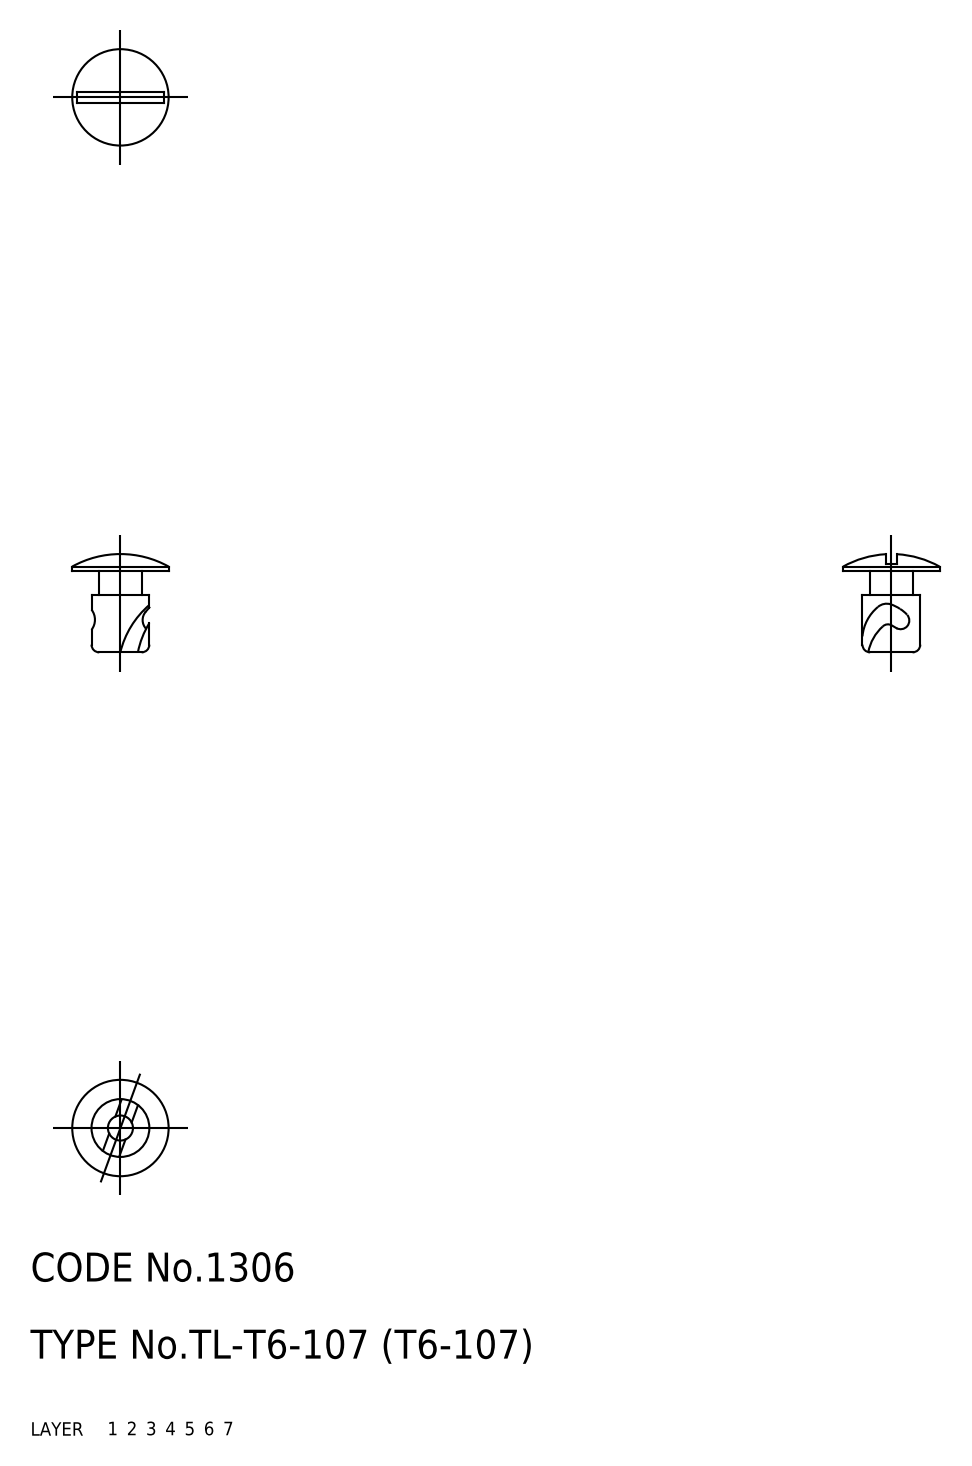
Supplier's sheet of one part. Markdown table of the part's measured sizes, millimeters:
| quantity | value |
| --- | --- |
| part name | 67113149 |
| STEP written by | CADfix (AUTOMOTIVE_DESIGN) |
| units | millimeters |
| bodies | 1 solid, 35 faces (0 planar, 0 cylindrical, 35 other) |
| overall size | 10.18 × 10 × 10 |
| volume | 225 mm³ |
| surface area | 392 mm² |
